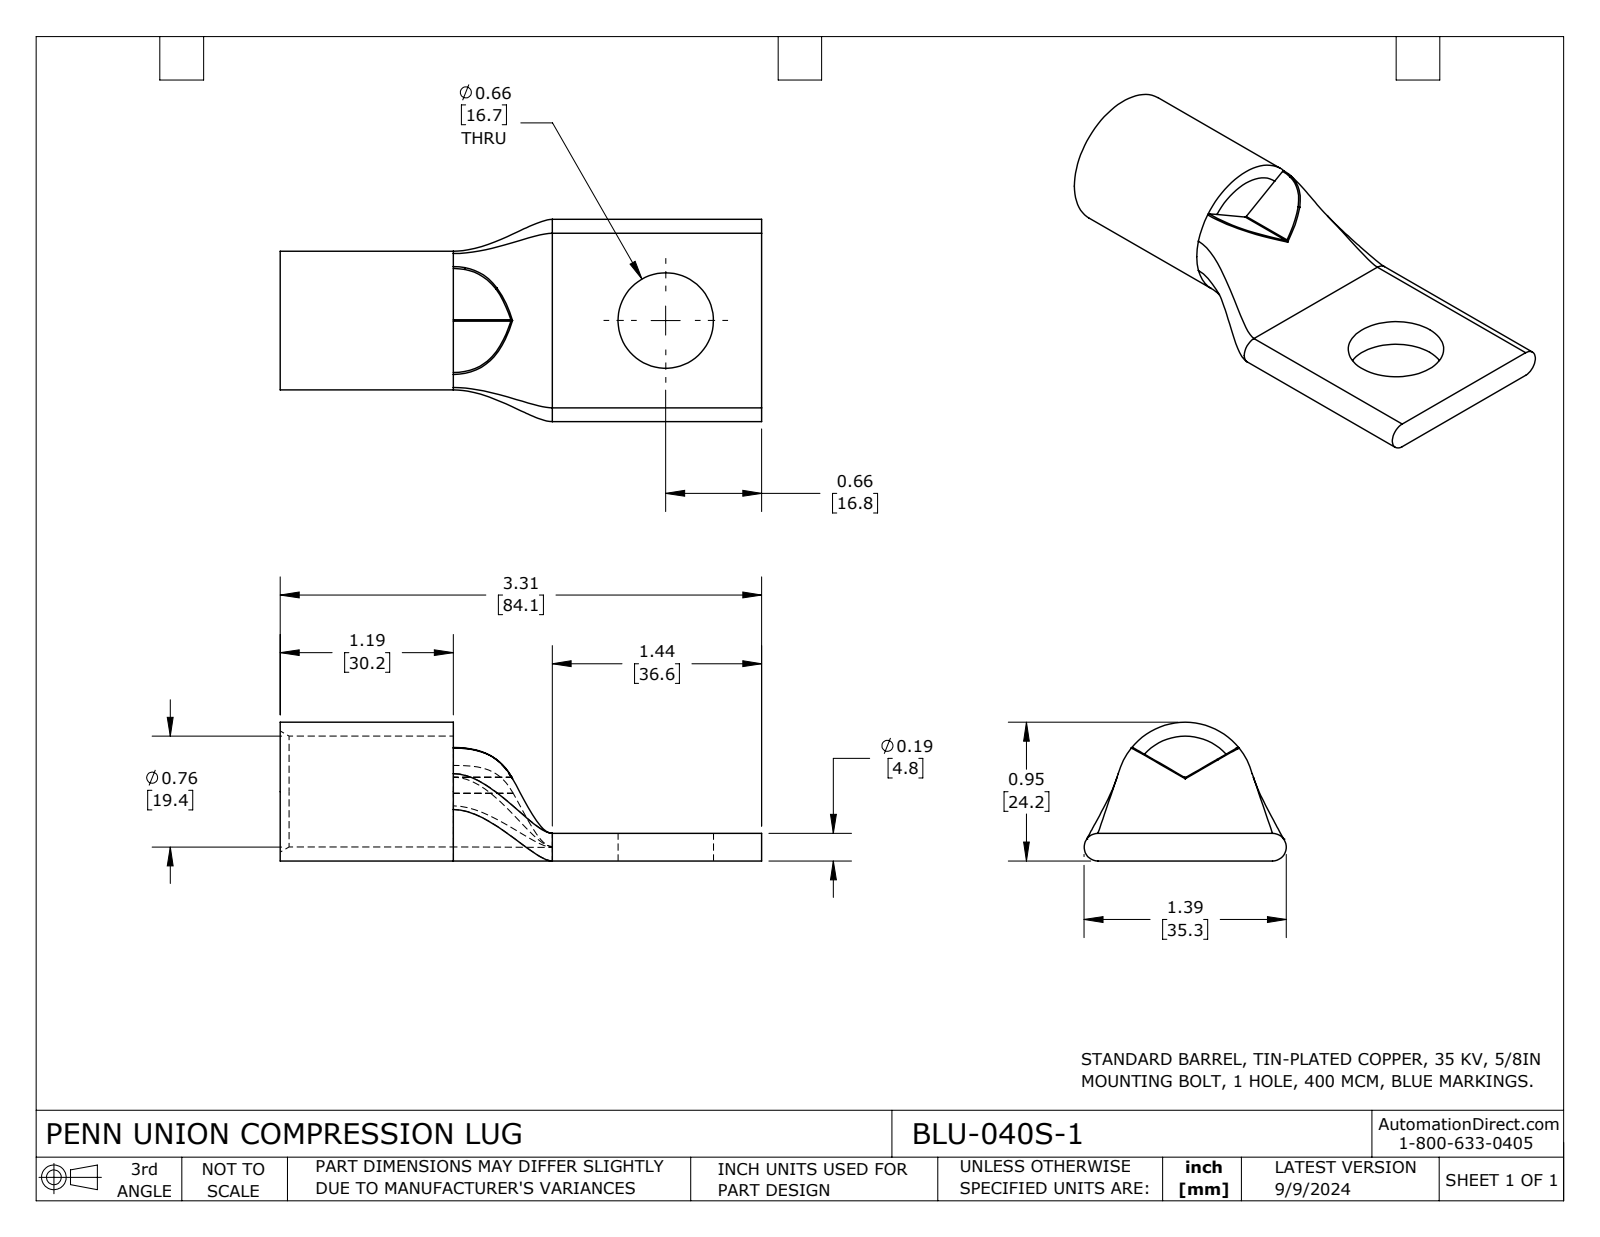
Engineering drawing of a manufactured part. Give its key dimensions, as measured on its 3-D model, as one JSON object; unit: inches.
{"part_name": "BLU-040S-1", "step_written_by": "SolidWorks 2023 (CONFIG_CONTROL_DESIGN)", "units": "inches", "bodies": {"solids": 1, "faces": 37, "planar": 11, "cylindrical": 11, "other": 15}, "overall_size": [3.31, 1.39, 0.953], "volume_in3": 0.771, "surface_area_in2": 15.14, "round_holes": [[0.656, 1], [0.762, 1]], "round_bosses_or_shafts": [[0.953, 1]], "partial_cylinders_radius": [[0.01, 2], [0.095, 2]], "face_to_face_distances": [0.19, 0.095, 3.31, 1.19, 2.12, 1.87, 0.68, 1.44]}
